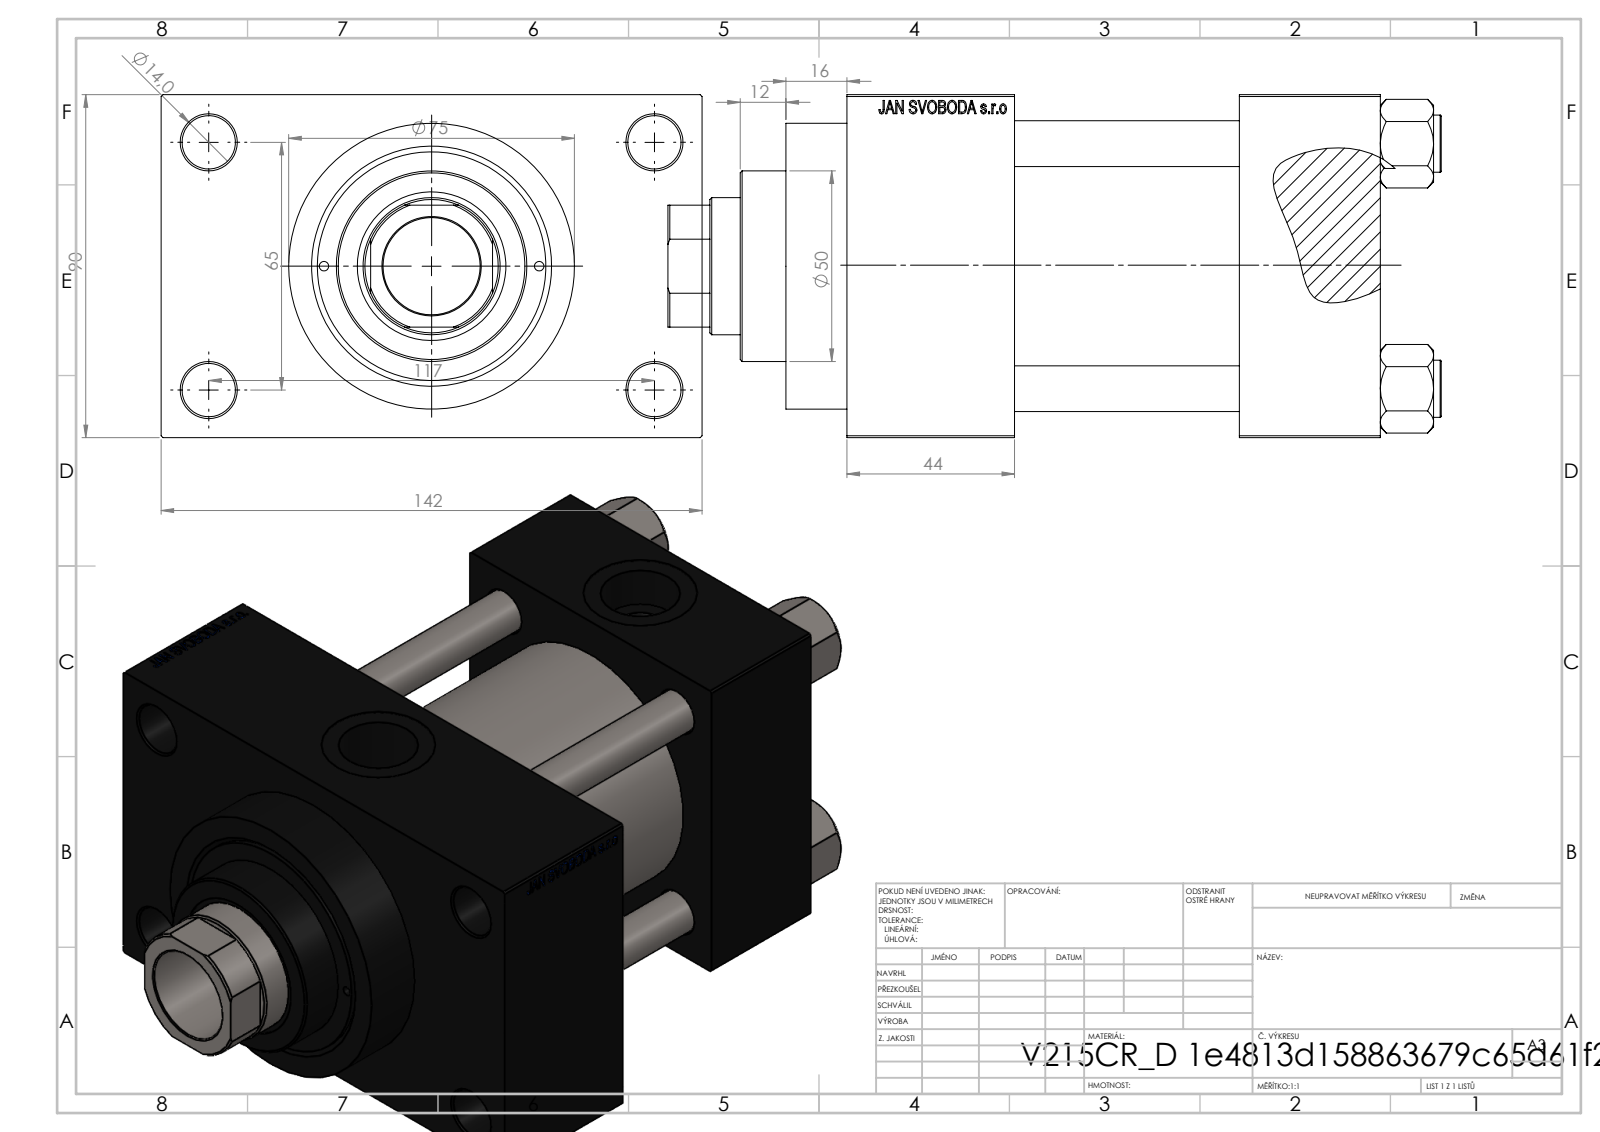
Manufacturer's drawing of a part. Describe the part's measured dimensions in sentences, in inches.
The part is named "V215CR_D_TYCINKA; V215_VC_A; V215CR_VCP_D; NUT_M5_D (+1 more)". Its 3-D file was written by "SolidWorks 2019 (CONFIG_CONTROL_DESIGN)". It is 11 solids with 1112 faces: 499 planar, 93 cylindrical and 520 other. Overall it measures 7.992 by 5.591 by 3.543 inches. Its volume is 68.35 cubic inches and its surface area 316.2 square inches. Round holes: 4 of diameter 0.472, 4 of diameter 0.551, 2 of diameter 0.098, 2 of diameter 0.276, 2 of diameter 0.825, 2 of diameter 1.181, 1 of diameter 1.004, 1 of diameter 1.417, 1 of diameter 1.535, 1 of diameter 1.969, 1 of diameter 2.362, 1 of diameter 2.48. Round bosses or shafts: 4 of diameter 0.591, 1 of diameter 2.953, 1 of diameter 2.717. Partial cylindrical surfaces (rounded edges, fillets, slot ends): 1 of radius 0.689. The main face-to-face distances are 3.543, 2.323, 1.457, 3.78, 5.512, 4.055, 1.732, 1.024, 4.567, 5.591. The hole center spacings are 1.037, 1.275, 1.748, 1.79, 2.531, 2.635, 2.694, 2.748.
